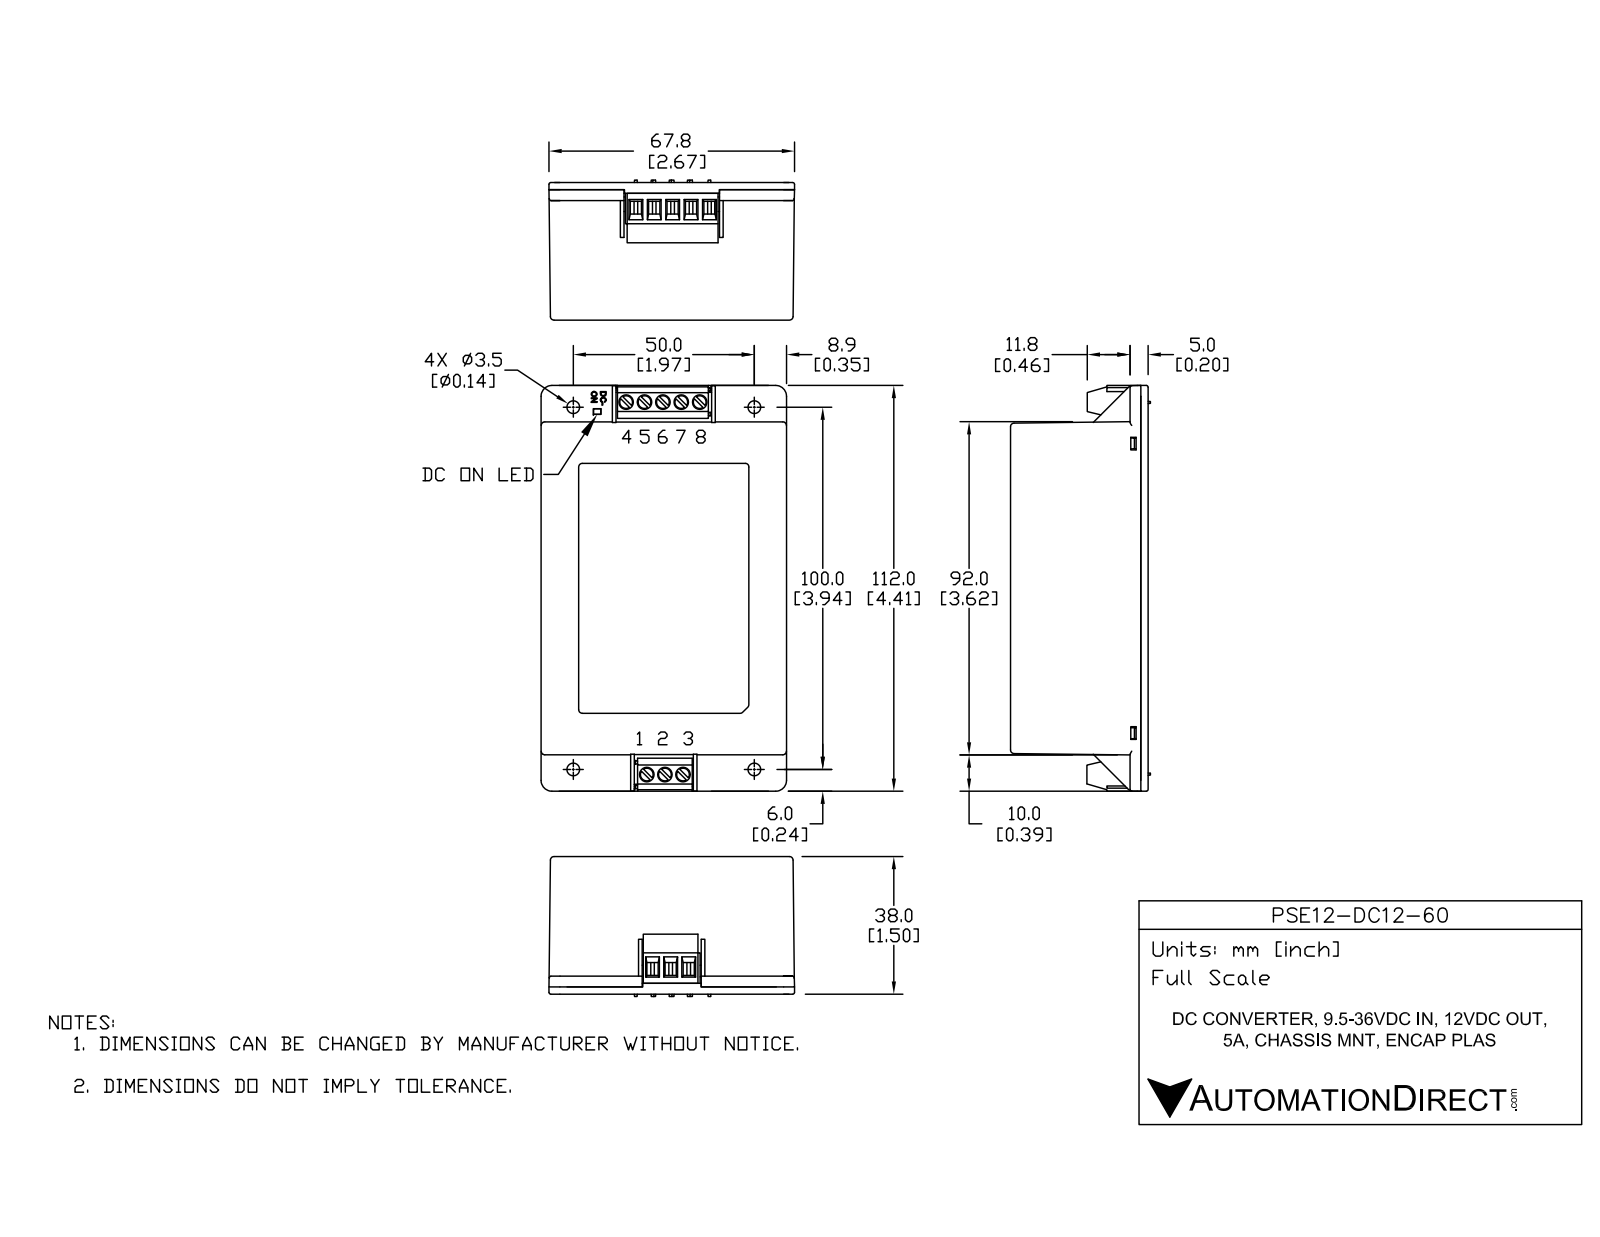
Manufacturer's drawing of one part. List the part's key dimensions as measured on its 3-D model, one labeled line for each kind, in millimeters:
Part name (STEP PRODUCT): PSE12-DC12-60
STEP written by: SolidWorks 2015 (AUTOMOTIVE_DESIGN)
Units: millimetres
Bodies: 0 solids, 390 faces (282 planar, 89 cylindrical, 19 other)
Overall size (bounding box): 112.92 × 69.3 × 37.06
Round holes (diameter × count): ⌀4 ×10, ⌀3.5 ×4, ⌀2.46 ×1, ⌀4.08 ×1, ⌀6.5 ×1
Round bosses / shafts (diameter × count): ⌀1.5 ×4, ⌀5 ×1
Partial cylindrical surfaces — rounded edges, fillets, slot ends (radius × count): R1 ×17, R0.5 ×8, R2.15 ×4, R2.65 ×4, R3 ×4, R3.25 ×3
Main face-to-face distances: 1, 0.98, 35, 34, 0.7, 1.02, 1.7, 33.3, 34.99, 33.99
Hole centre spacings: 5.08, 10.16, 50, 102.13, 102.29, 5, 15.24, 100
